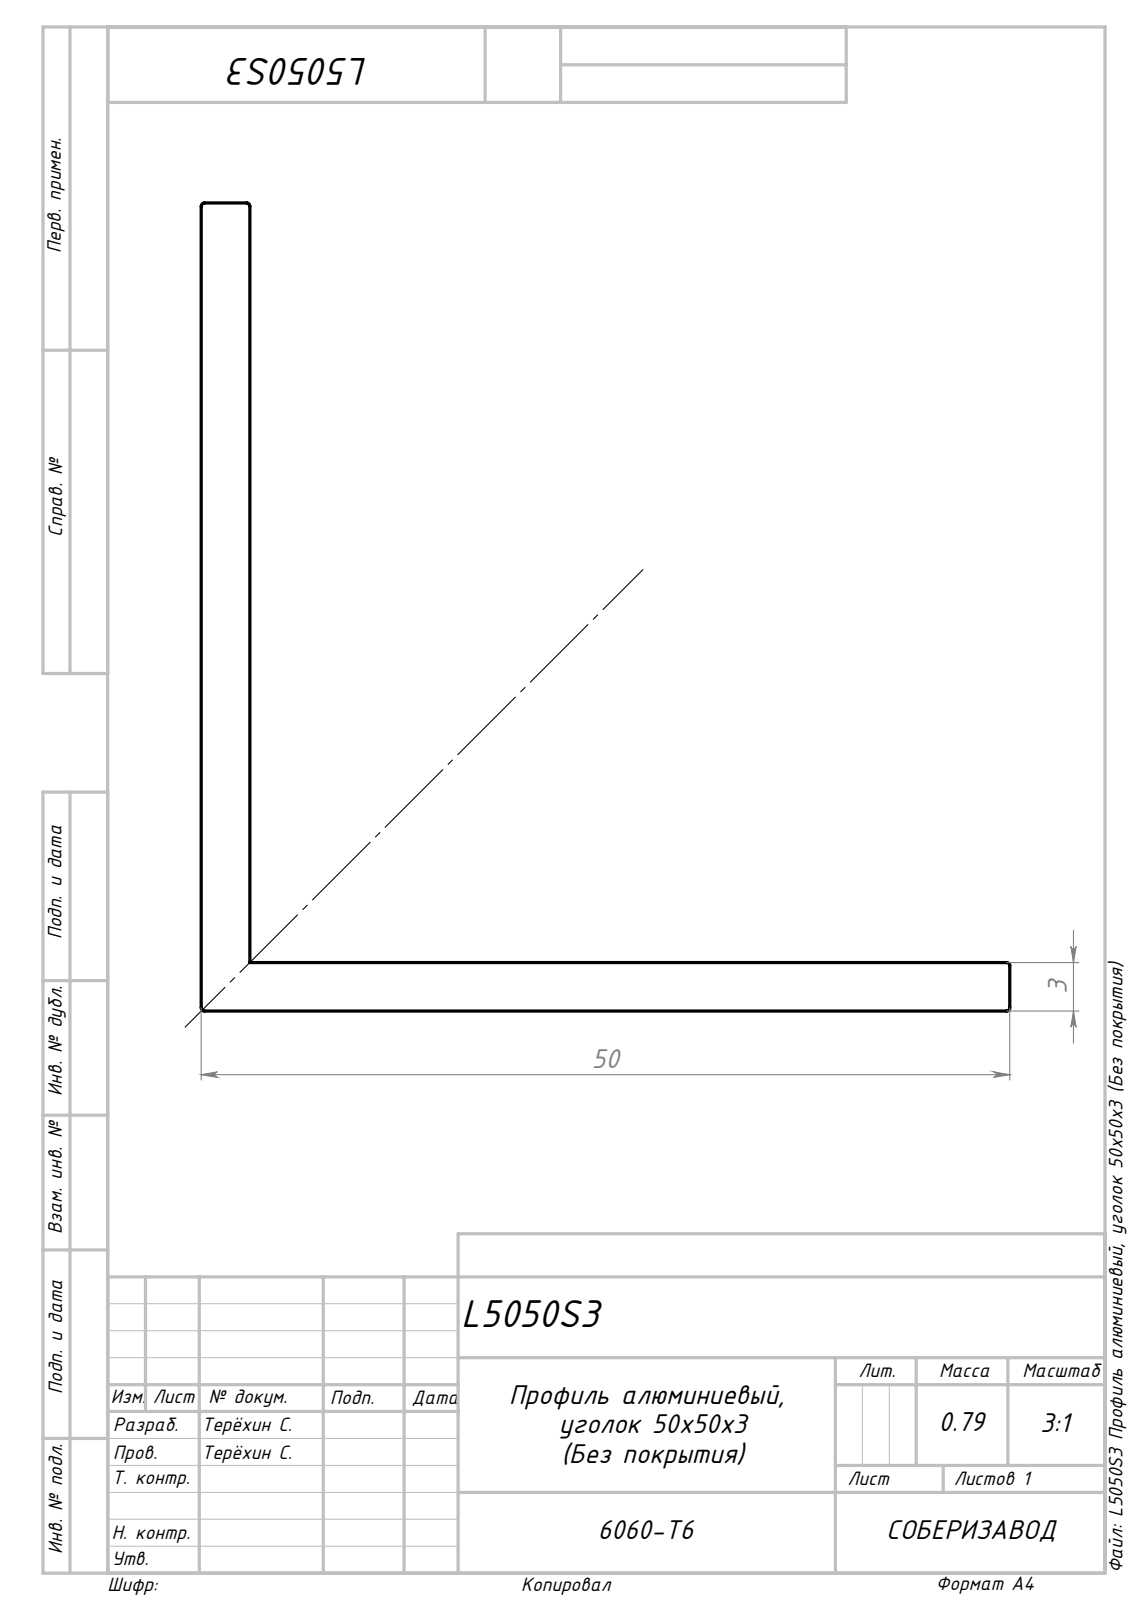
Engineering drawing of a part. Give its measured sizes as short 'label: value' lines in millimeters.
name: Сборка8; L5050S3 Профиль алюминиевый, уголок 50x50x3 (Без покрытия)_00
written by: SolidWorks 2024 (AUTOMOTIVE_DESIGN)
unit: mm
bodies: 1 solid, 13 faces (8 planar, 5 cylindrical, 0 other)
size: 1000 × 50 × 50
volume: 290 957 mm³; area: 200 153 mm²
rounds: 5× R0.2
face distances: 3, 50, 47, 1000
